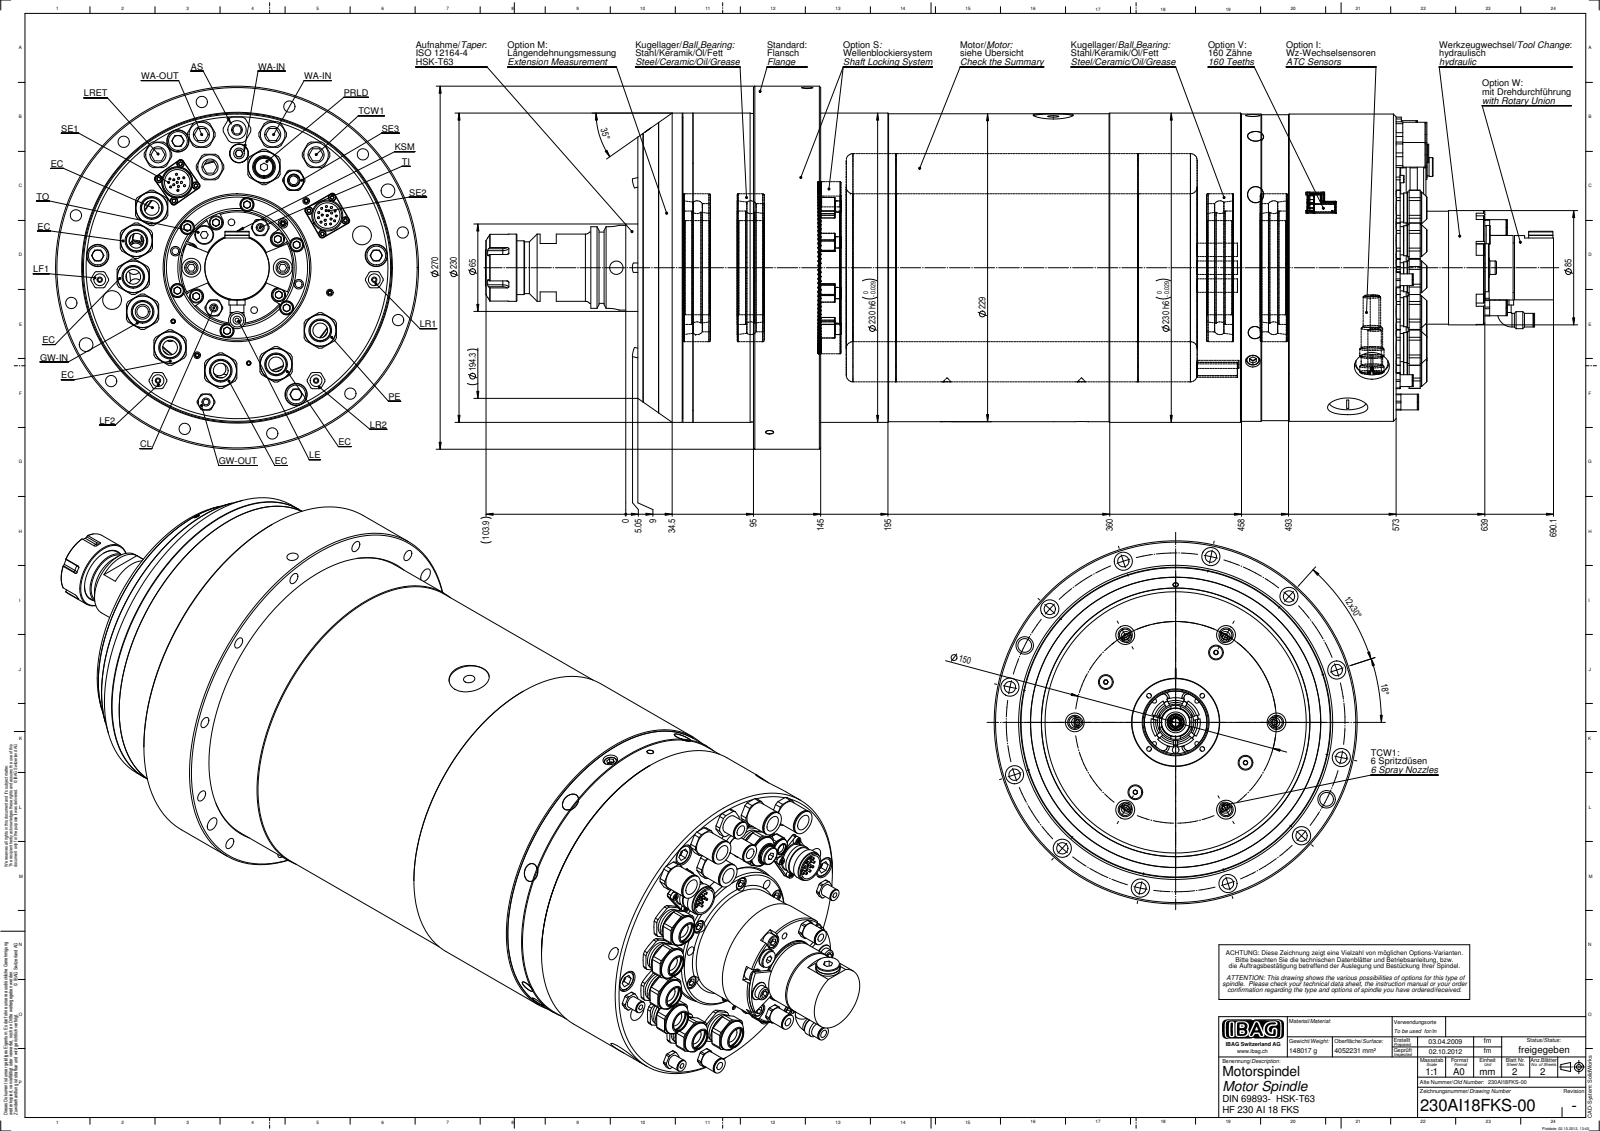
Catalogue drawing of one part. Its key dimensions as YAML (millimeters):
part_name: "230AI18FKS-00"
step_written_by: "SolidWorks 2012 (CONFIG_CONTROL_DESIGN)"
units: millimeters
bodies: {solids: 0, faces: 1827, planar: 639, cylindrical: 827, other: 361}
overall_size: [794.46, 270, 270]
round_holes:
  - {diameter: 5, count: 12}
  - {diameter: 8.4, count: 12}
  - {diameter: 13.5, count: 12}
  - {diameter: 11, count: 11}
  - {diameter: 21.31, count: 9}
  - {diameter: 14, count: 8}
  - {diameter: 15.1, count: 8}
  - {diameter: 10.4, count: 6}
  - {diameter: 30, count: 6}
  - {diameter: 12, count: 5}
  - {diameter: 4, count: 4}
  - {diameter: 6, count: 4}
round_bosses_or_shafts:
  - {diameter: 1.5, count: 29}
  - {diameter: 23.7, count: 9}
  - {diameter: 22.3, count: 9}
  - {diameter: 20.96, count: 9}
  - {diameter: 10, count: 8}
  - {diameter: 7, count: 7}
  - {diameter: 5.5, count: 7}
  - {diameter: 18.3, count: 5}
partial_cylinders:
  - {radius: 1, count: 12}
  - {radius: 13.2, count: 9}
  - {radius: 6.6, count: 7}
  - {radius: 10.25, count: 6}
  - {radius: 5.5, count: 5}
  - {radius: 4, count: 4}
  - {radius: 8, count: 4}
  - {radius: 8.25, count: 1}
face_to_face_distances: [41, 564, 523, 449, 408, 115, 4, 37, 445, 560]
hole_center_spacings: [126, 75, 218.24, 65.22, 178.19, 243.41, 54.9, 94.1]
